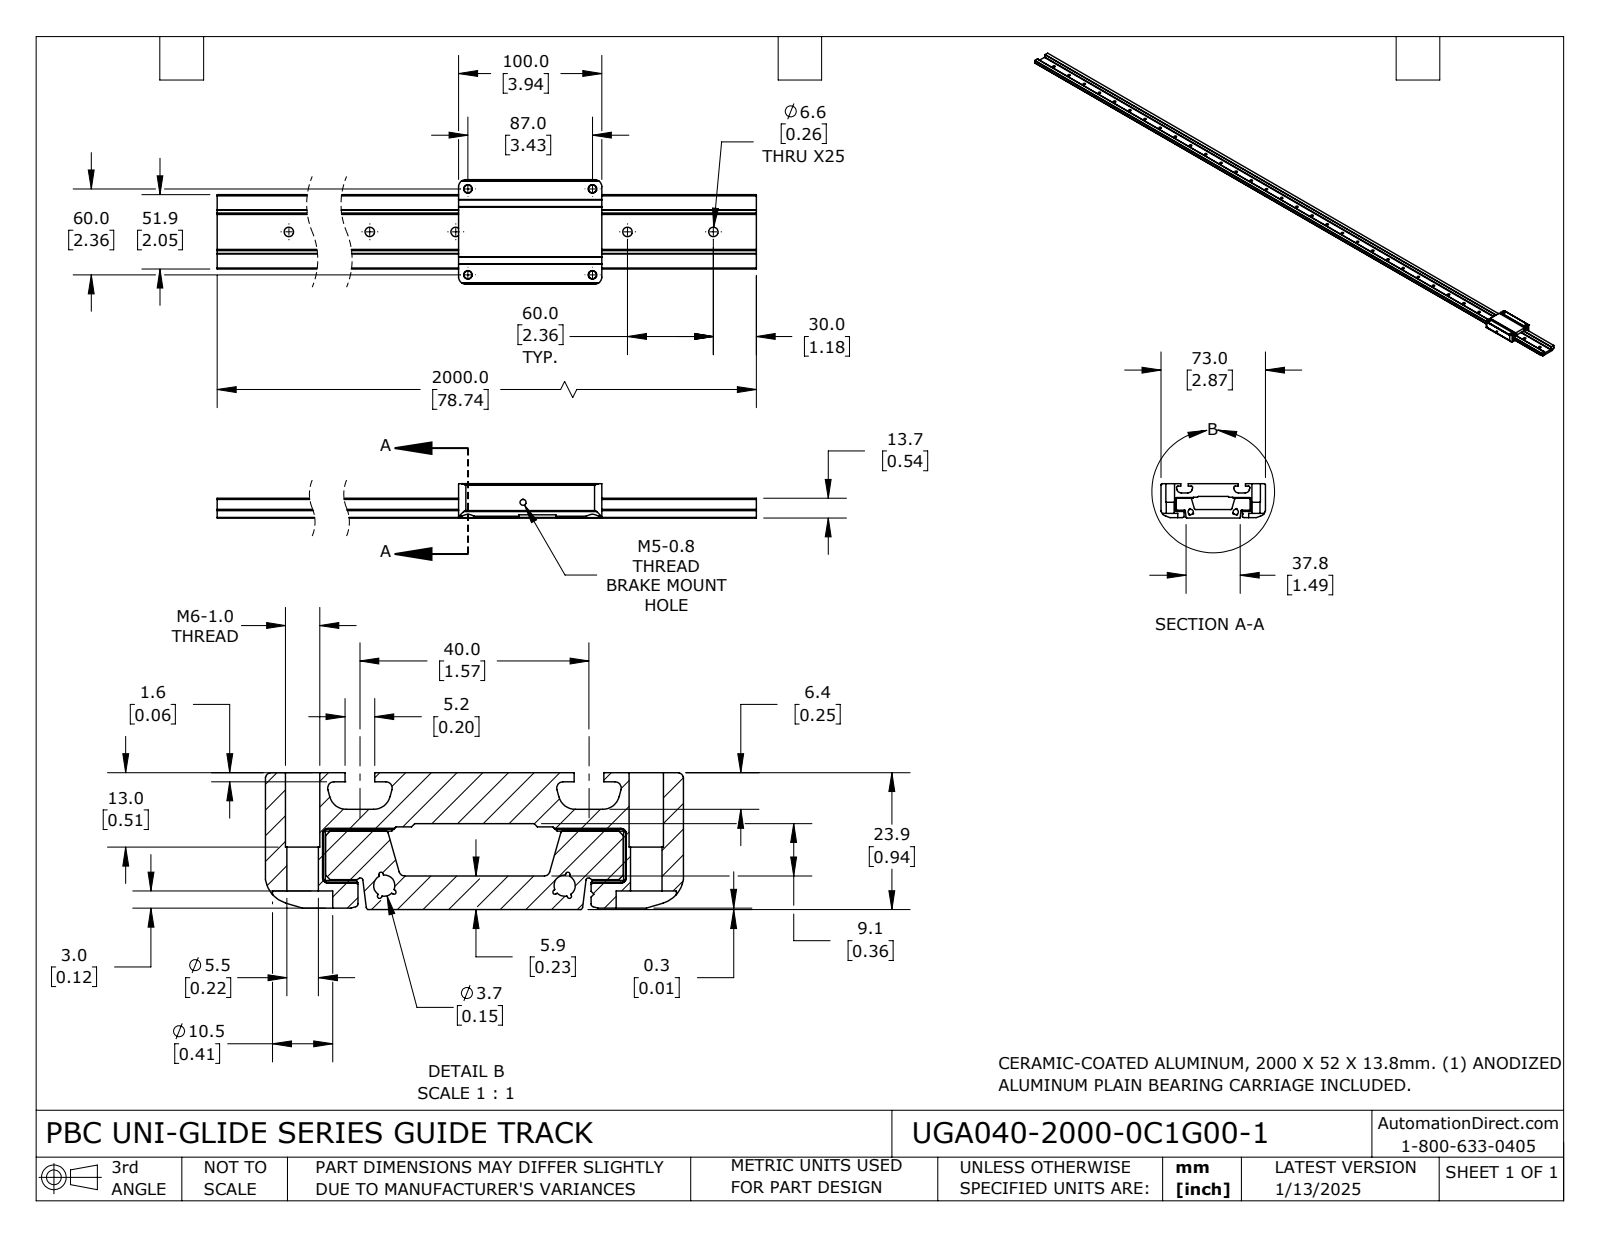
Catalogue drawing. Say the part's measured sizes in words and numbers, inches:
The part is named "UGA040-2000-0C1G00-1; UGA040-2000-0C1G00-1_RAIL; UGA040-2000-0C1G00-1_CARRIAGE". Its 3-D file was written by "SolidWorks 2023 (CONFIG_CONTROL_DESIGN)". It is 10 solids with 448 faces: 214 planar, 215 cylindrical and 19 other. Overall it measures 78.74 by 2.874 by 0.941 inches. Its volume is 52.91 cubic inches and its surface area 595.7 square inches. Round holes: 33 of diameter 0.261, 4 of diameter 0.098, 4 of diameter 0.118, 4 of diameter 0.217, 4 of diameter 0.236, 4 of diameter 0.413, 2 of diameter 0.146, 1 of diameter 0.165. Partial cylindrical surfaces (rounded edges, fillets, slot ends): 8 of radius 0.039, 8 of radius 0.094, 6 of radius 0.015, 6 of radius 0.02, 6 of radius 0.197, 4 of radius 0.035, 4 of radius 0.043, 4 of radius 0.118. The main face-to-face distances are 0.231, 0.539, 0.308, 0.333, 0.207, 0.024, 2.045, 0.941, 0.734, 0.71. The hole center spacings are 2.362, 4.724, 7.087, 9.449, 11.811, 14.173, 16.535, 18.898.
